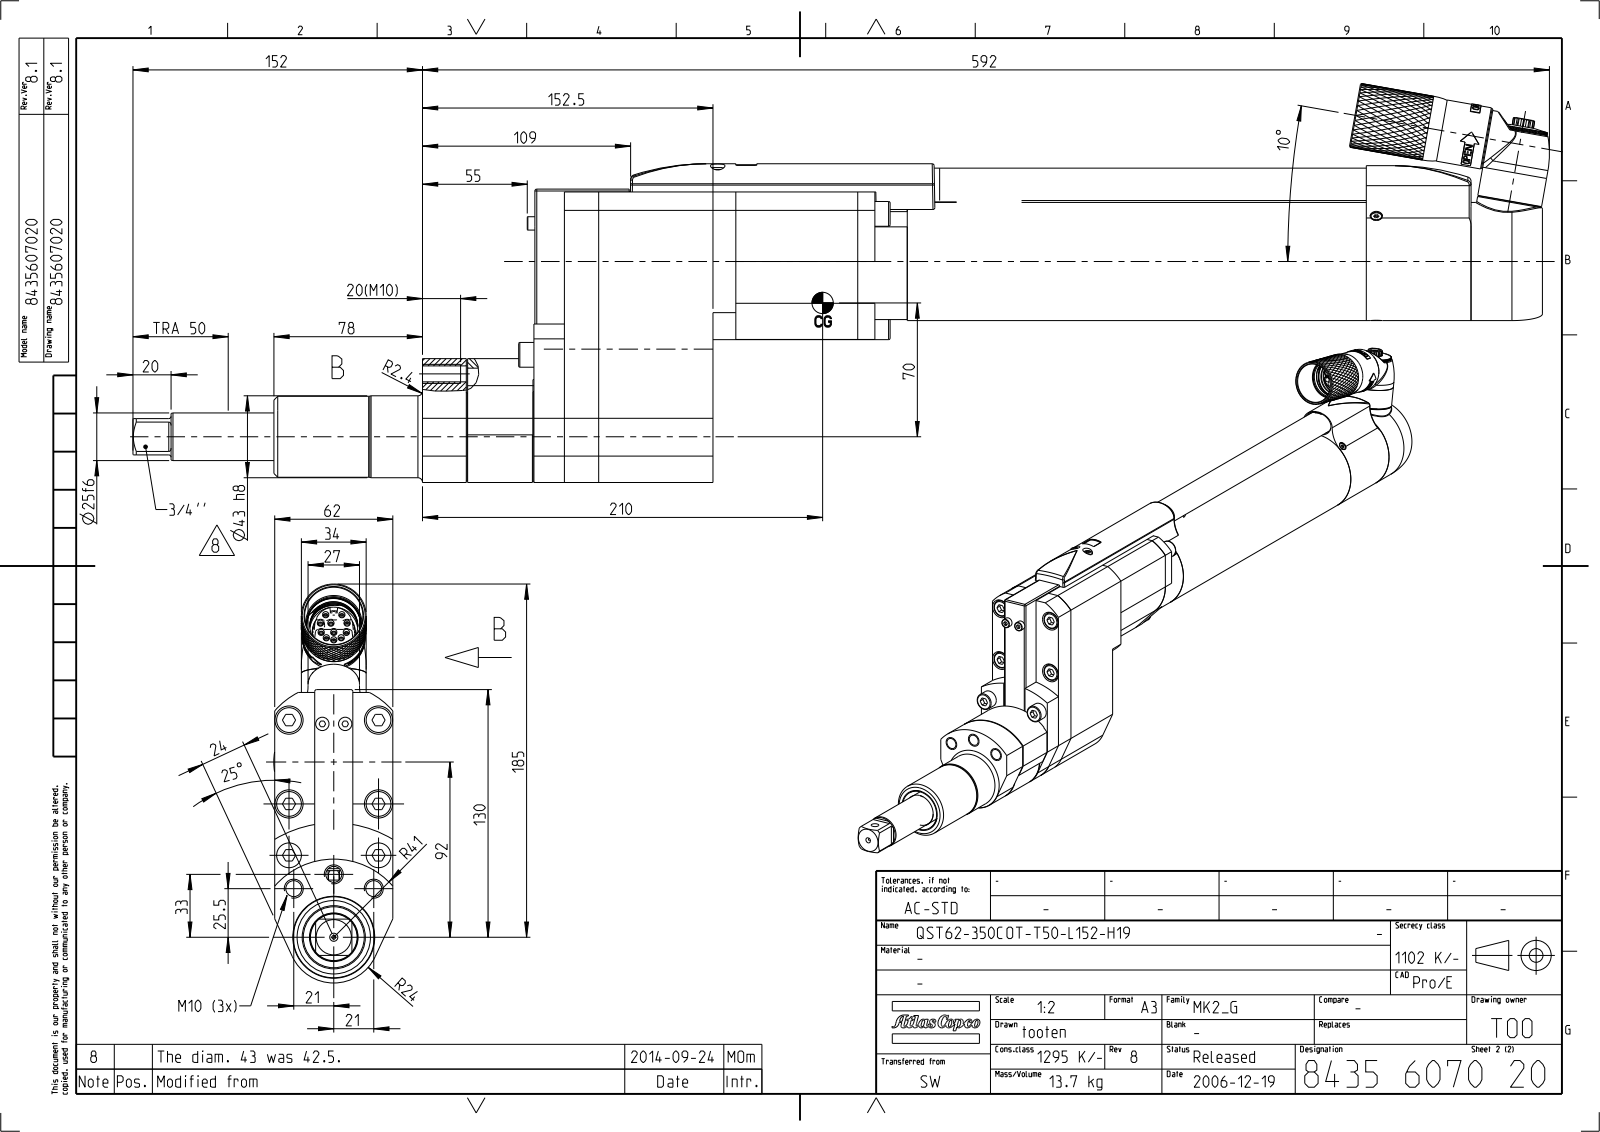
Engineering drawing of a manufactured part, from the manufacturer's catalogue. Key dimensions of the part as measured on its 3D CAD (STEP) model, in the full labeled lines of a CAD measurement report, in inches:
Part name (STEP PRODUCT): 4230260301; 4230260311_ASM; 4230265400; 0219110017 (+8 more)
STEP written by: CREO PARAMETRIC BY PTC INC, 2018100 (CONFIG_CONTROL_DESIGN)
Units: inches
Bodies: 38 solids, 3026 faces (1122 planar, 975 cylindrical, 929 other)
Overall size (bounding box): 29.277 × 8.243 × 2.441
Volume: 87.2 in³ · Surface area: 789.8 in²
Round holes (diameter × count): ⌀0.354 ×10, ⌀0.13 ×7, ⌀0.272 ×7, ⌀0.335 ×7, ⌀0.128 ×4, ⌀0.177 ×4, ⌀0.262 ×4, ⌀0.551 ×4, ⌀0.075 ×3, ⌀0.138 ×3, ⌀0.154 ×3, ⌀0.213 ×3
Round bosses / shafts (diameter × count): ⌀0.315 ×10, ⌀0.512 ×9, ⌀0.118 ×5, ⌀0.276 ×4, ⌀0.197 ×4, ⌀0.157 ×4, ⌀1.339 ×3, ⌀0.22 ×3
Partial cylindrical surfaces — rounded edges, fillets, slot ends (radius × count): R0.011 ×18, R0.02 ×18, R0.039 ×10, R0.079 ×8, R0.008 ×4, R0.031 ×4, R0.047 ×4, R0.207 ×4
Main face-to-face distances: 2.441, 0.709, 1.614, 0.827, 0.748, 0.039, 3.543, 2.362, 2.933, 3.071
Hole centre spacings: 1.85, 0.256, 0.797, 1.267, 2.159, 0.472, 0.657, 0.886
